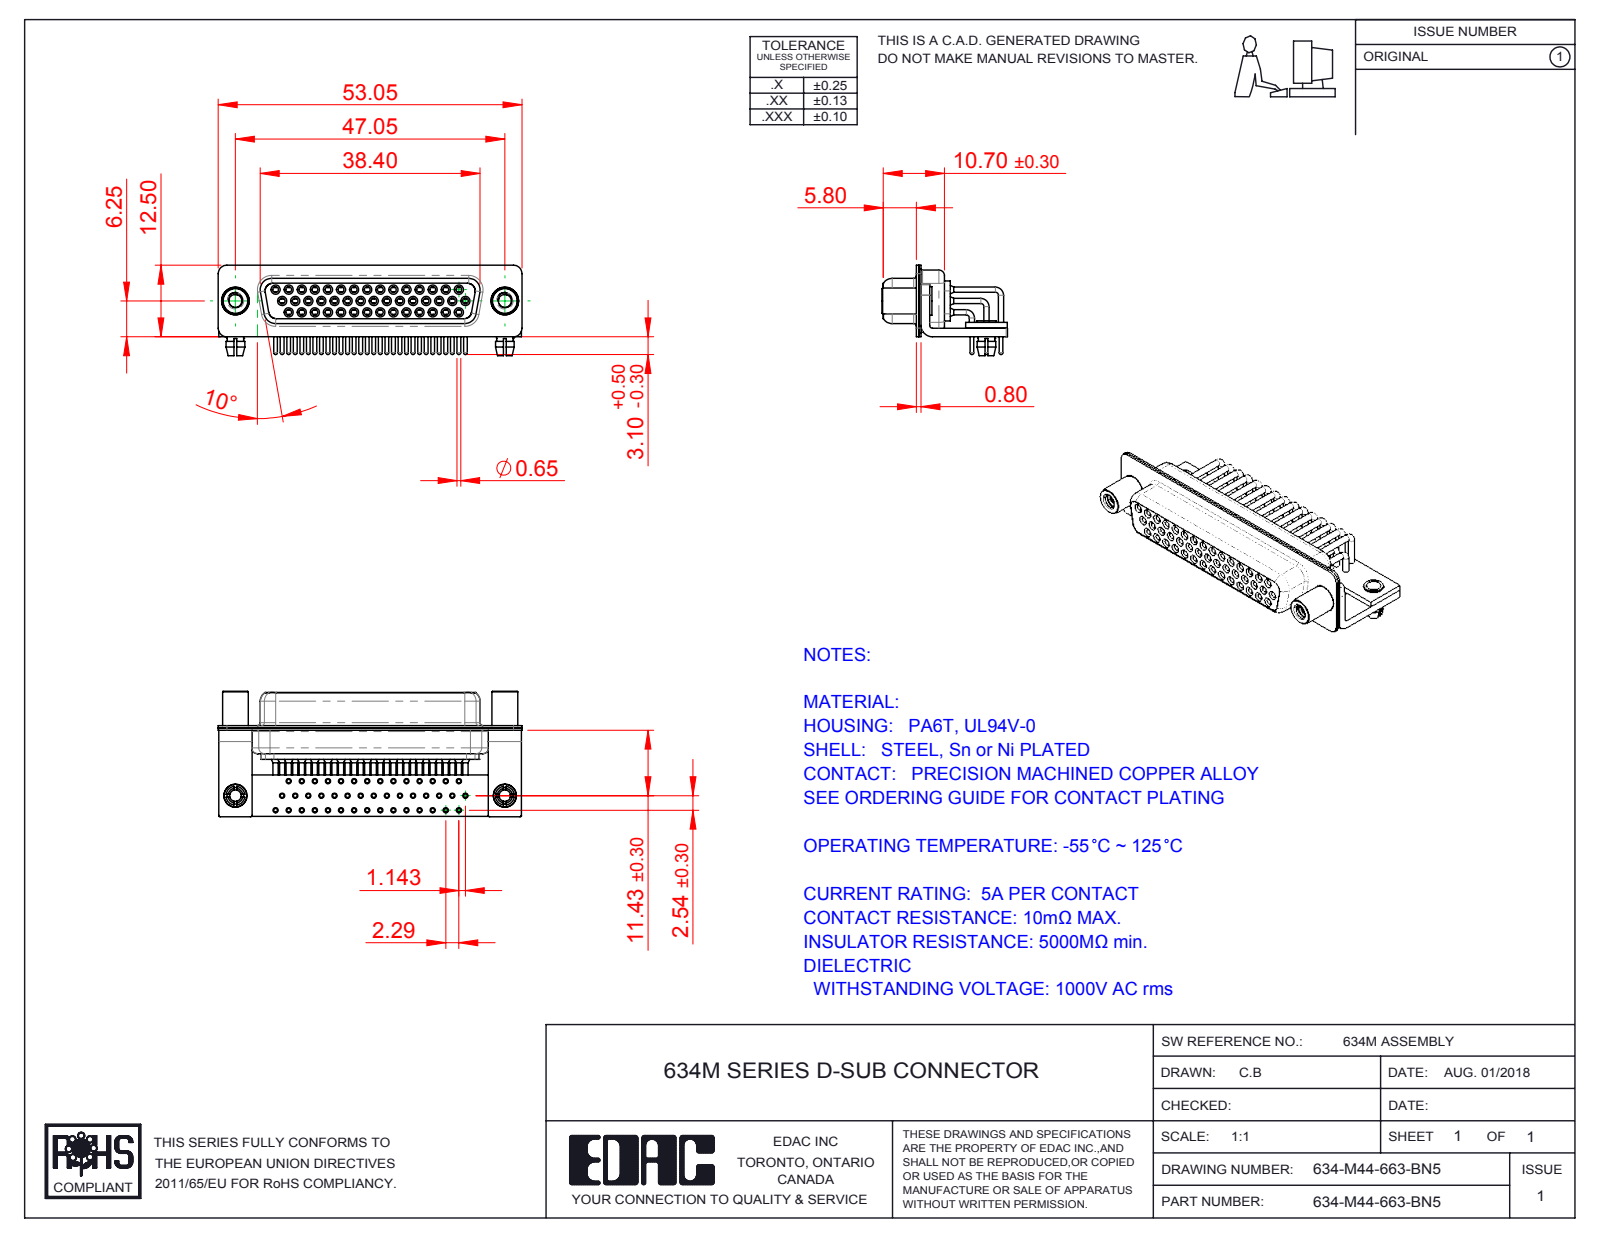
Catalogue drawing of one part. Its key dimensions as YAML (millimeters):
part_name: "634M Stabilizer Board_44 Contacts; 634M Shell Front_44 Contacts; 634M Board Lock; 634M 4-40 Threaded Standoff (+7 more)"
step_written_by: "SolidWorks 2016 (CONFIG_CONTROL_DESIGN)"
units: millimeters
bodies: {solids: 54, faces: 2891, planar: 803, cylindrical: 1333, other: 755}
overall_size: [53.05, 21.9, 15.8]
volume: 4630
surface_area: 15156
round_holes:
  - {diameter: 2, count: 46}
  - {diameter: 0.9, count: 44}
  - {diameter: 1, count: 44}
  - {diameter: 1.1, count: 44}
  - {diameter: 1.7, count: 44}
  - {diameter: 1.8, count: 44}
  - {diameter: 2.26, count: 2}
  - {diameter: 2.5, count: 2}
  - {diameter: 3.2, count: 2}
  - {diameter: 4, count: 2}
  - {diameter: 4.8, count: 2}
round_bosses_or_shafts:
  - {diameter: 1.6, count: 44}
  - {diameter: 1.5, count: 44}
  - {diameter: 0.9, count: 44}
  - {diameter: 0.65, count: 44}
  - {diameter: 5, count: 2}
  - {diameter: 4.9, count: 2}
  - {diameter: 4.5, count: 2}
  - {diameter: 4, count: 2}
partial_cylinders:
  - {radius: 0.25, count: 16}
  - {radius: 1.5, count: 16}
  - {radius: 2, count: 13}
  - {radius: 1.35, count: 8}
  - {radius: 1.6, count: 8}
  - {radius: 0.5, count: 5}
  - {radius: 0.6, count: 4}
  - {radius: 0.65, count: 4}
face_to_face_distances: [0.4, 2.3, 1.9, 1, 0.8, 9.35, 8.5, 1.5, 1.45, 8.95]
hole_center_spacings: [2.28, 2.29, 4.57, 6.86, 11.43, 3.96, 8.24, 9.14]
